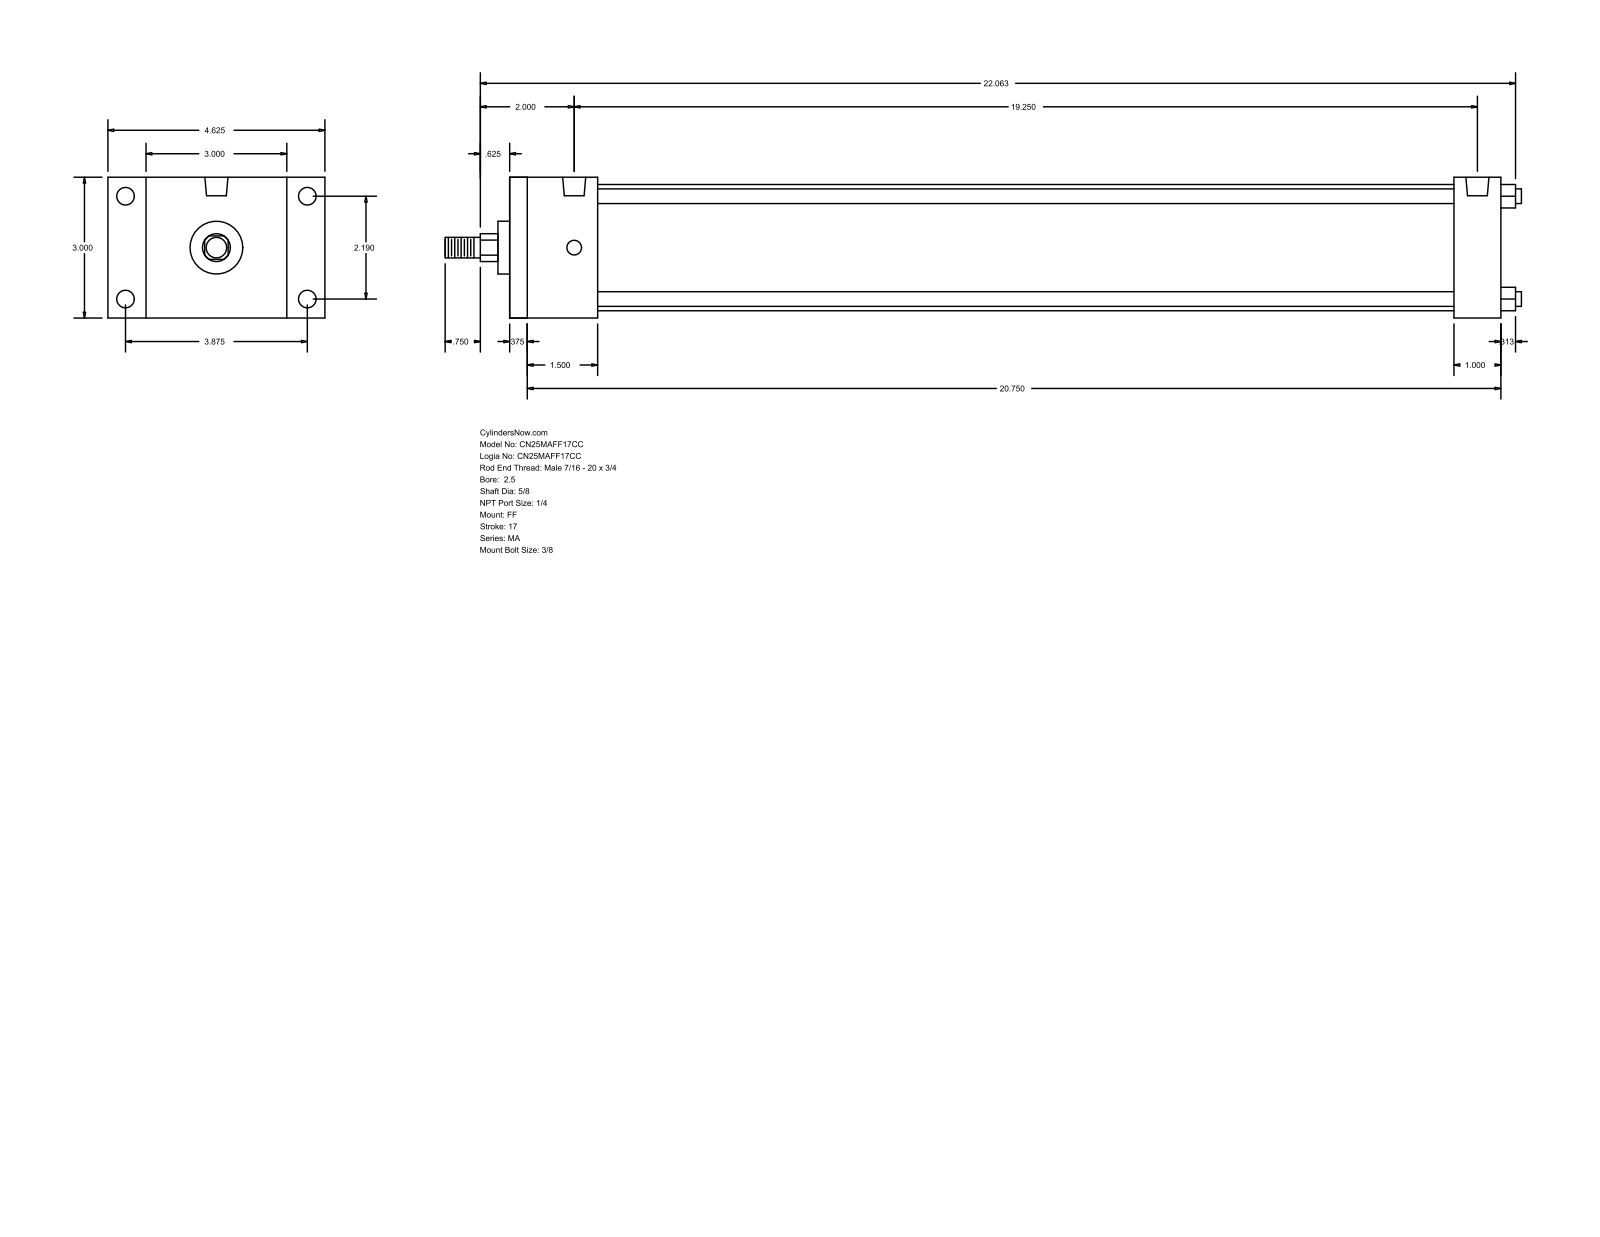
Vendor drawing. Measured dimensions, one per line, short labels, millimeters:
name: MA_FF__0250_0.625
written by: GSSL Pune (CONFIG_CONTROL_DESIGN)
unit: mm
bodies: 0 solids, 92 faces (64 planar, 28 cylindrical, 0 other)
size: 582.61 × 117.47 × 76.2
holes: 4× ⌀7.94, 4× ⌀9.53, 2× ⌀12.49
bosses: 4× ⌀7.94, 1× ⌀68.33, 1× ⌀28.57, 1× ⌀15.88, 1× ⌀11.11
rounds: 1× R7.54
face distances: 76.2, 536.57, 527.05, 9.52, 25.4, 47.62, 511.17, 38.1, 501.65, 463.55
hole spacings: 55.62, 98.42, 113.05, 488.95
